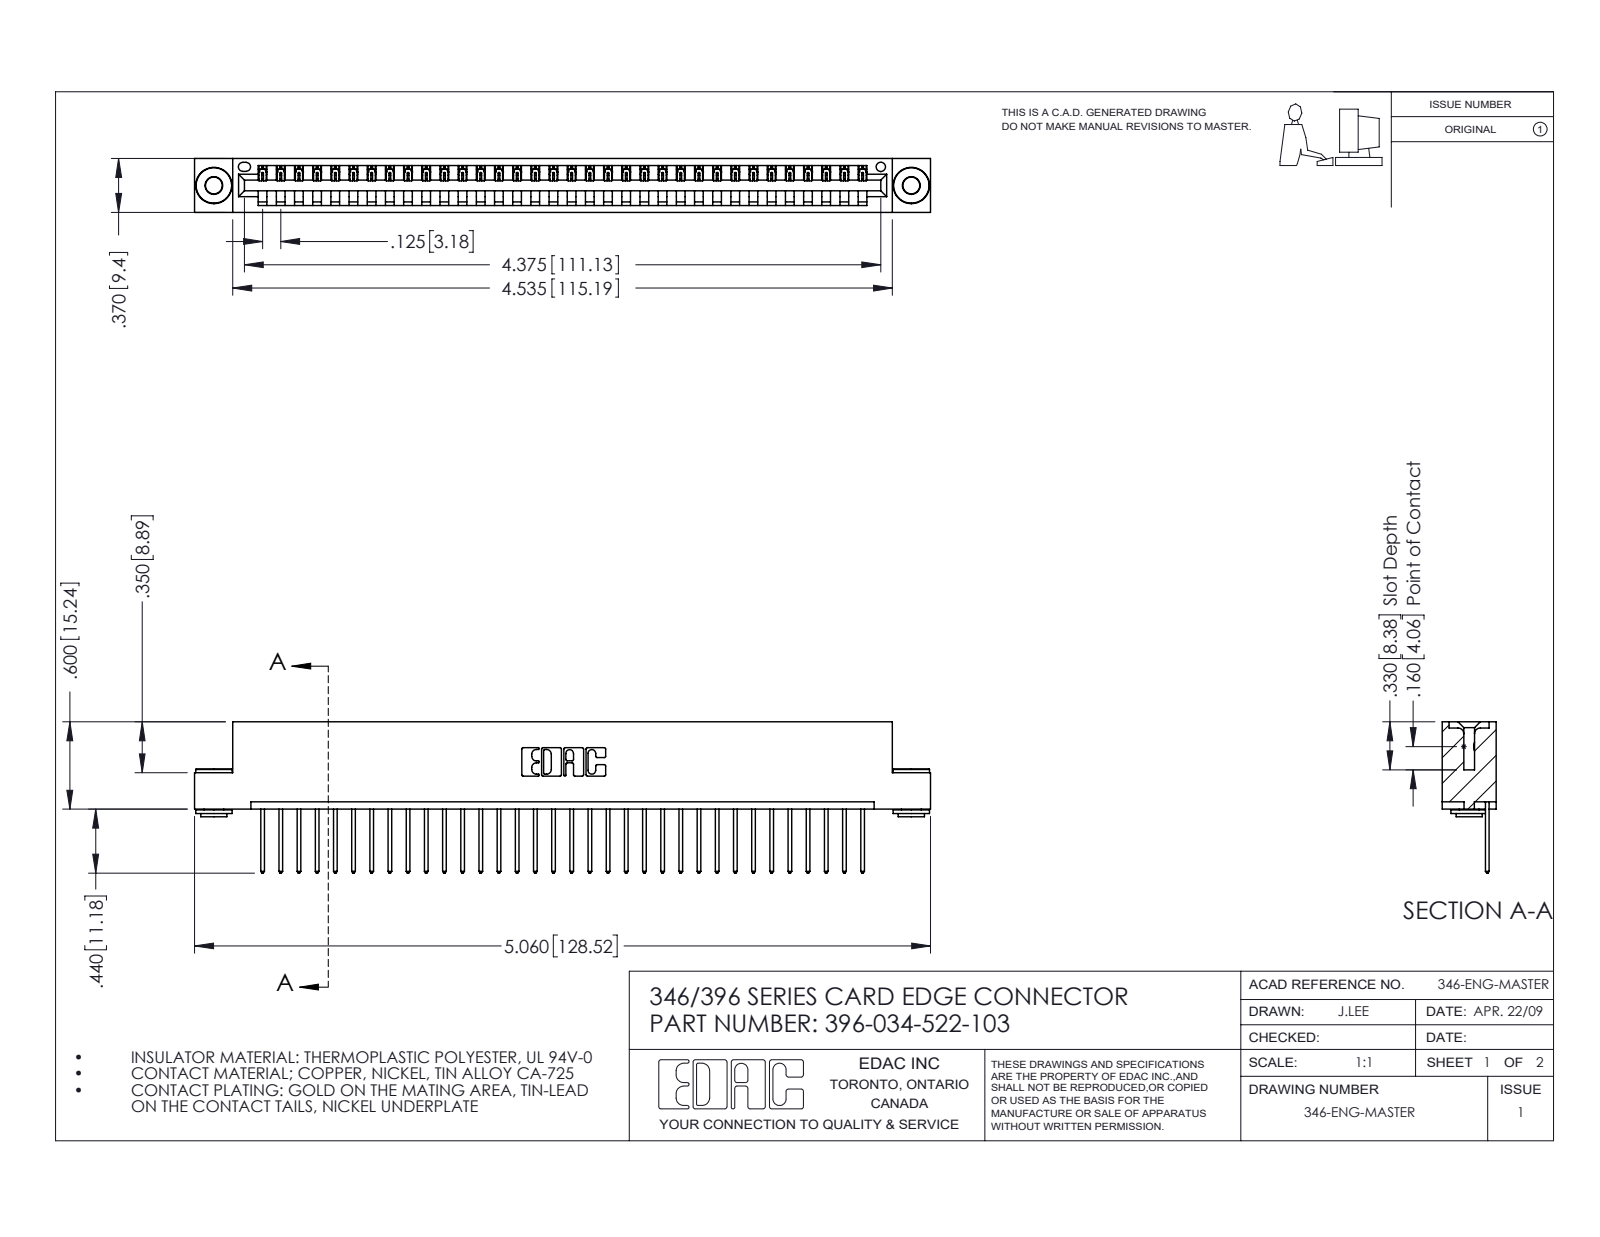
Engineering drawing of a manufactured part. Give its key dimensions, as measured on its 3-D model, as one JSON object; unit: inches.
{"part_name": "346 Part_Flush Mounting Lugs - 0.156 Dia-TH; 345-250-002_345-250-002-102; 396-034-522-103; 345-292-001_345-293-122", "step_written_by": "SolidWorks 2016 (CONFIG_CONTROL_DESIGN)", "units": "inches", "bodies": {"solids": 37, "faces": 2132, "planar": 1446, "cylindrical": 678, "other": 8}, "overall_size": [5.06, 1.04, 0.37], "volume_in3": 0.749, "surface_area_in2": 24.17, "round_holes": [[0.116, 2], [0.156, 2], [0.064, 1]], "round_bosses_or_shafts": [[0.25, 2], [0.18, 2], [0.136, 2]], "partial_cylinders_radius": [[0.006, 68], [0.01, 68], [0.01, 22], [0.007, 6], [0.031, 6], [0.026, 3], [0.031, 2], [0.04, 2]], "face_to_face_distances": [0.048, 0.322, 0.25, 0.37, 0.025, 0.072, 0.298, 0.148, 0.222, 0.1], "hole_center_spacings": [0.246, 4.587, 4.795]}
